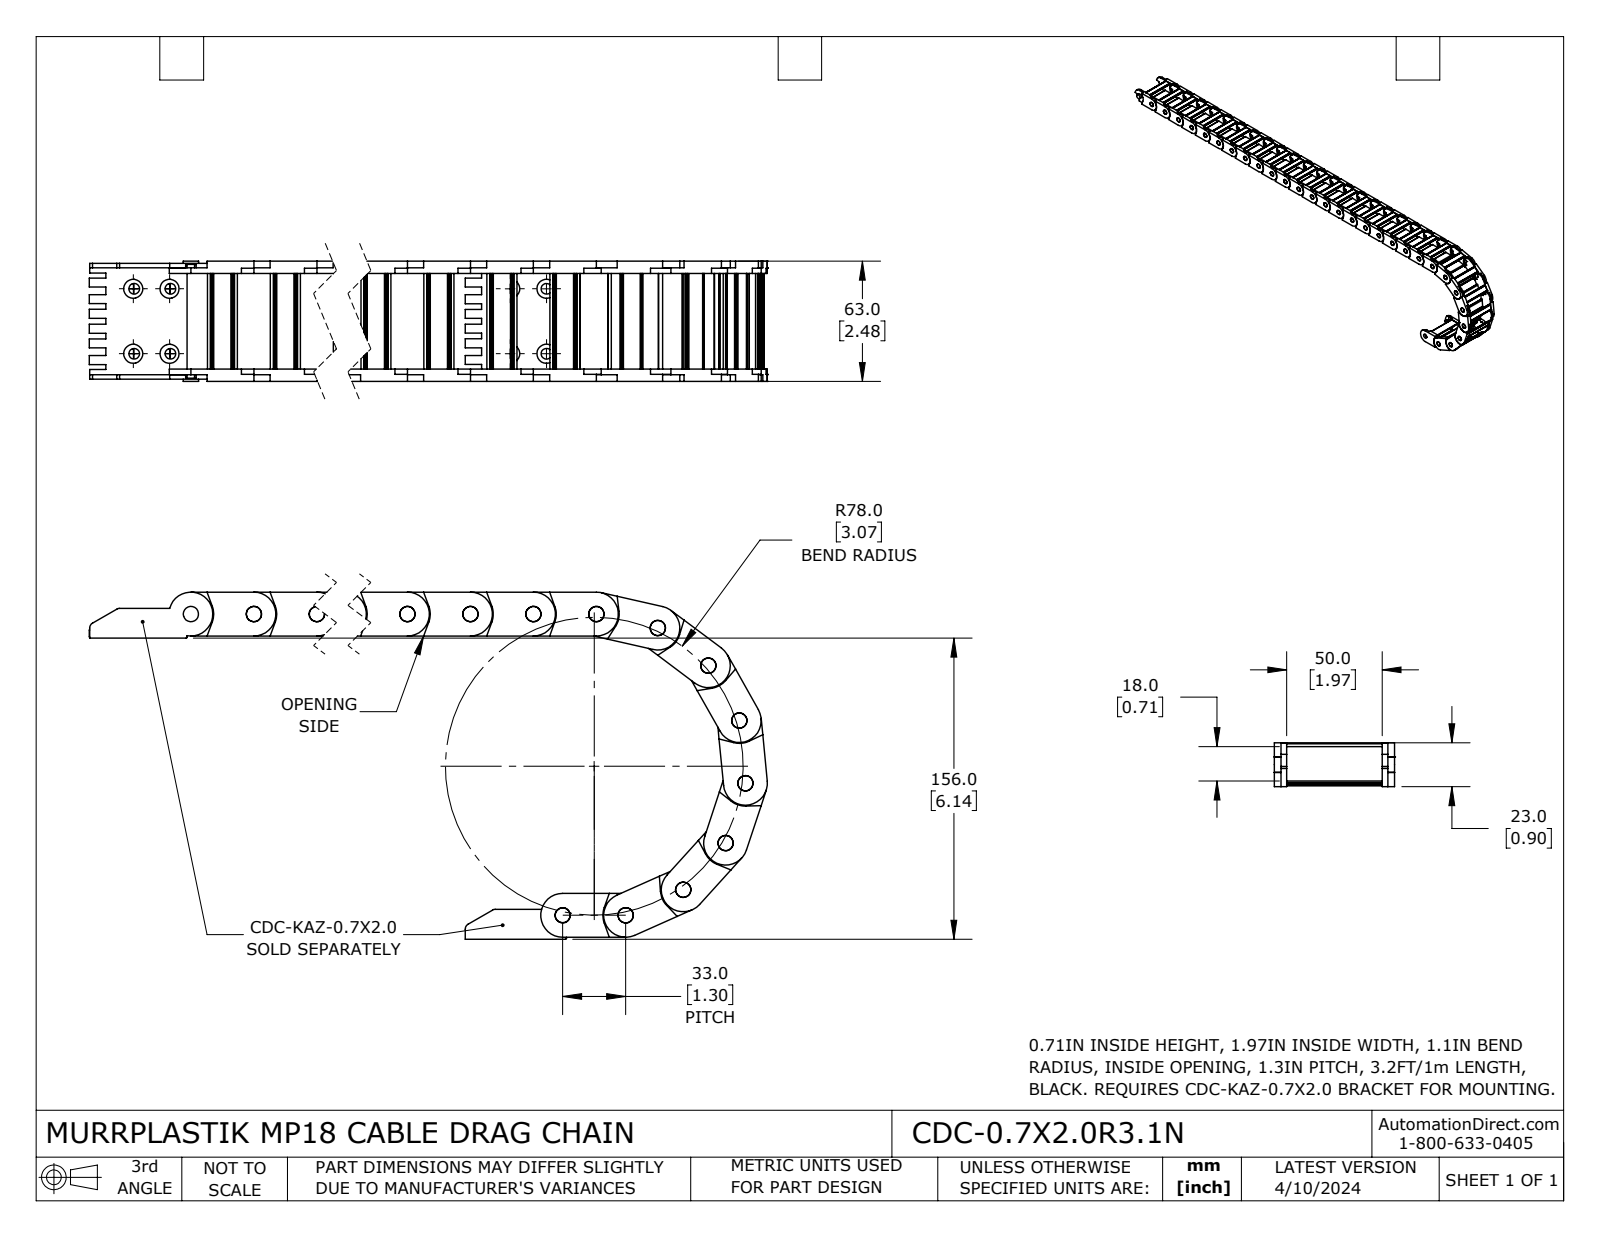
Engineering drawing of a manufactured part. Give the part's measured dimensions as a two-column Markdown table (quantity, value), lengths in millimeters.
| quantity | value |
| --- | --- |
| part name | CDC-0.7X2.0R3.1N |
| STEP written by | SolidWorks 2023 (CONFIG_CONTROL_DESIGN) |
| units | millimeters |
| bodies | 30 solids, 2370 faces (1110 planar, 1260 cylindrical, 0 other) |
| overall size | 826.89 × 180.72 × 63 |
| volume | 345 175 mm³ |
| surface area | 267 172 mm² |
| round holes (diameter × count) | 8 × 30 |
| round bosses / shafts (diameter × count) | 8 × 1 |
| partial cylindrical surfaces (radius × count) | 0.5 × 120, 1.5 × 120, 0.2 × 60, 0.3 × 60, 11.5 × 31, 11.95 × 31, 5 × 30, 5.45 × 30 |
| main face-to-face distances | 6.5, 56.5, 63, 3.5, 59.5, 3, 53, 3.7, 59.3, 55.8 |
| hole center spacings | 33, 66, 99, 132, 165, 198, 231, 264 |
